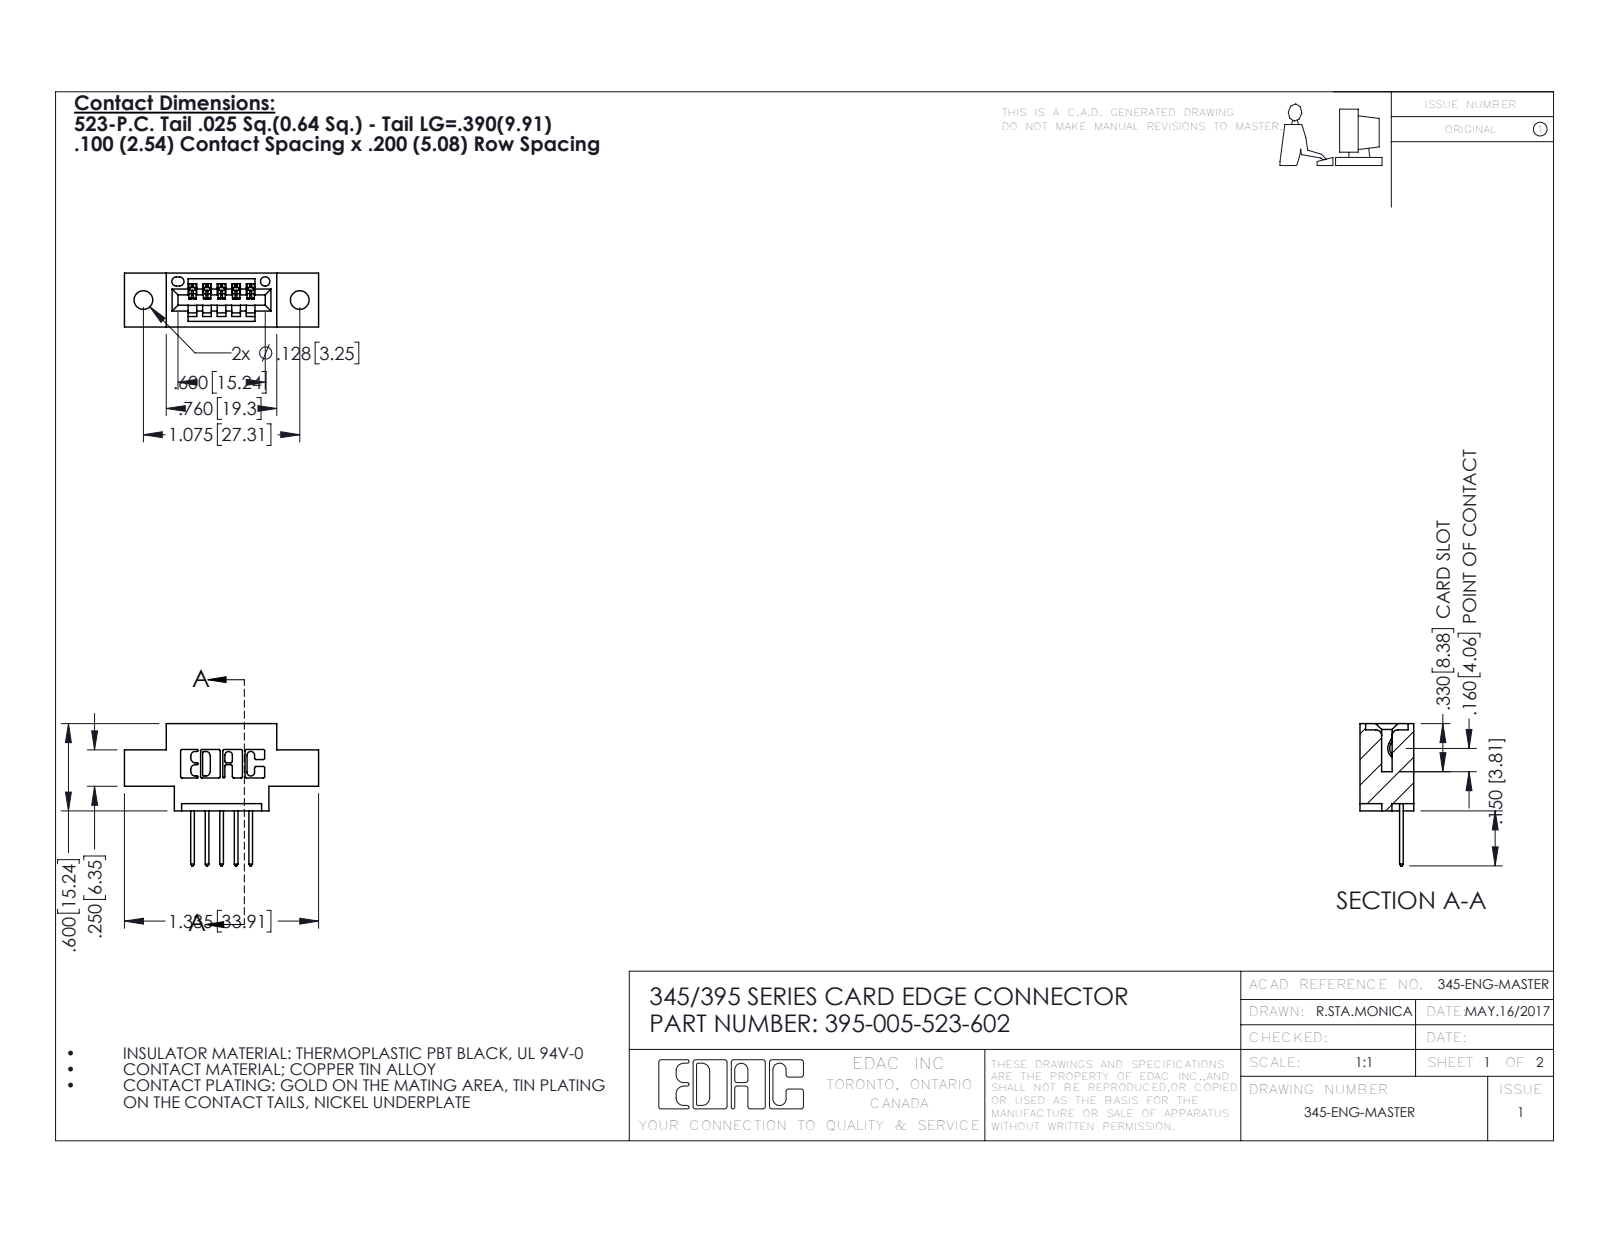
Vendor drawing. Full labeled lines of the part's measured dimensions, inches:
Part name (STEP PRODUCT): 395-005-523-602; 345-292-001_345-293-123; 345 Part_0.170 Offset - 0.128 Dia
STEP written by: SolidWorks 2016 (CONFIG_CONTROL_DESIGN)
Units: inches
Bodies: 6 solids, 420 faces (284 planar, 136 cylindrical, 0 other)
Overall size (bounding box): 1.335 × 0.977 × 0.37
Volume: 0.169 in³ · Surface area: 4.701 in²
Round holes (diameter × count): ⌀0.128 ×2, ⌀0.064 ×1
Partial cylindrical surfaces — rounded edges, fillets, slot ends (radius × count): R0.01 ×22, R0.006 ×10, R0.01 ×10, R0.007 ×6, R0.031 ×6, R0.026 ×3, R0.031 ×2, R0.04 ×2
Main face-to-face distances: 0.37, 0.2, 0.298, 0.072, 0.1, 0.025, 0.25, 0.098, 0.272, 0.06
Hole centre spacings: 0.27, 0.847, 1.075
